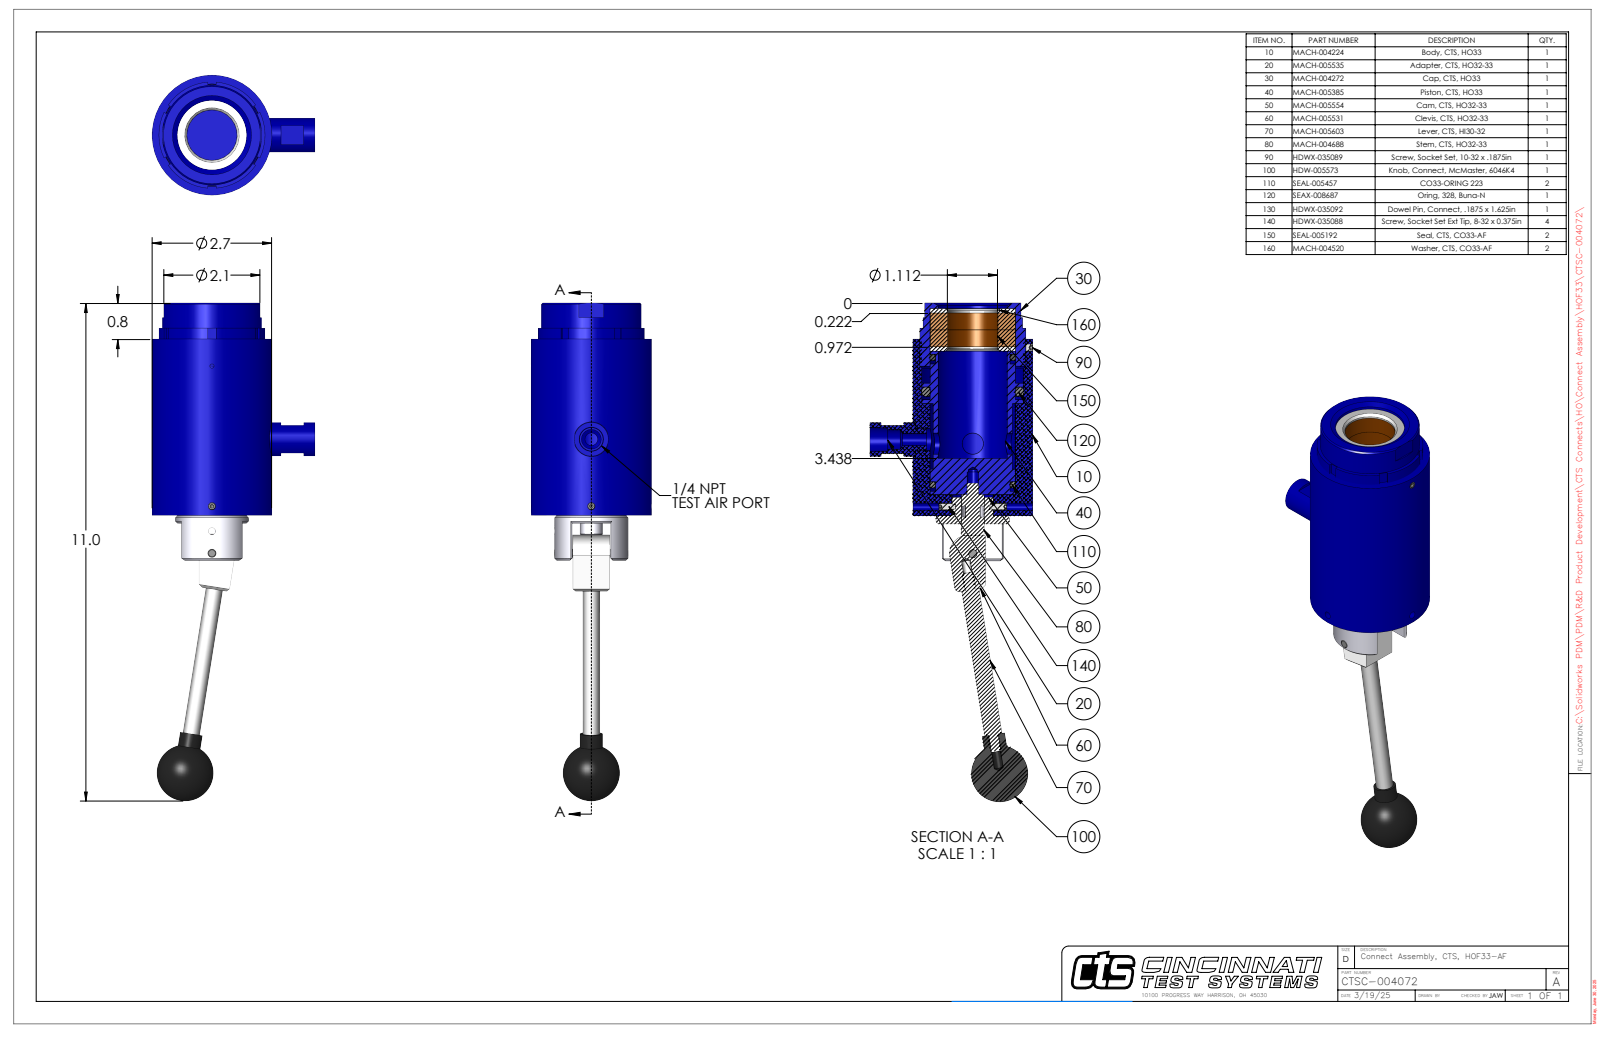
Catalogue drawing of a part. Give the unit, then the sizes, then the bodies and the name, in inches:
Units: inches
Overall size (bounding box): 11.035 × 3.6 × 2.65
Round holes (diameter × count): ⌀0.201 ×3, ⌀0.159 ×2, ⌀0.469 ×2, ⌀0.094 ×1, ⌀0.189 ×1, ⌀0.19 ×1, ⌀0.25 ×1, ⌀0.281 ×1, ⌀0.438 ×1, ⌀0.5 ×1, ⌀0.516 ×1, ⌀0.523 ×1
Round bosses / shafts (diameter × count): ⌀0.75 ×2, ⌀0.5 ×2, ⌀0.164 ×2, ⌀0.109 ×2, ⌀2.65 ×1, ⌀2.344 ×1, ⌀2.2 ×1, ⌀1.885 ×1
Partial cylindrical surfaces — rounded edges, fillets, slot ends (radius × count): R0.385 ×1, R0.4 ×1, R1.13 ×1, R1.195 ×1
Main face-to-face distances: 0.844, 0.094, 0.75, 3.736, 4.486, 0.375, 0.375, 4.111, 0.469, 3.642
Hole centre spacings: 0.093, 0.488, 1.713, 1.945, 2.033, 2.126, 2.433, 3.658
Volume: 22.13 in³ · Surface area: 138.8 in²
Bodies: 15 solids, 546 faces (179 planar, 226 cylindrical, 141 other)
Part name (STEP PRODUCT): CTSC-004072
STEP written by: SolidWorks 2023 (AUTOMOTIVE_DESIGN)
